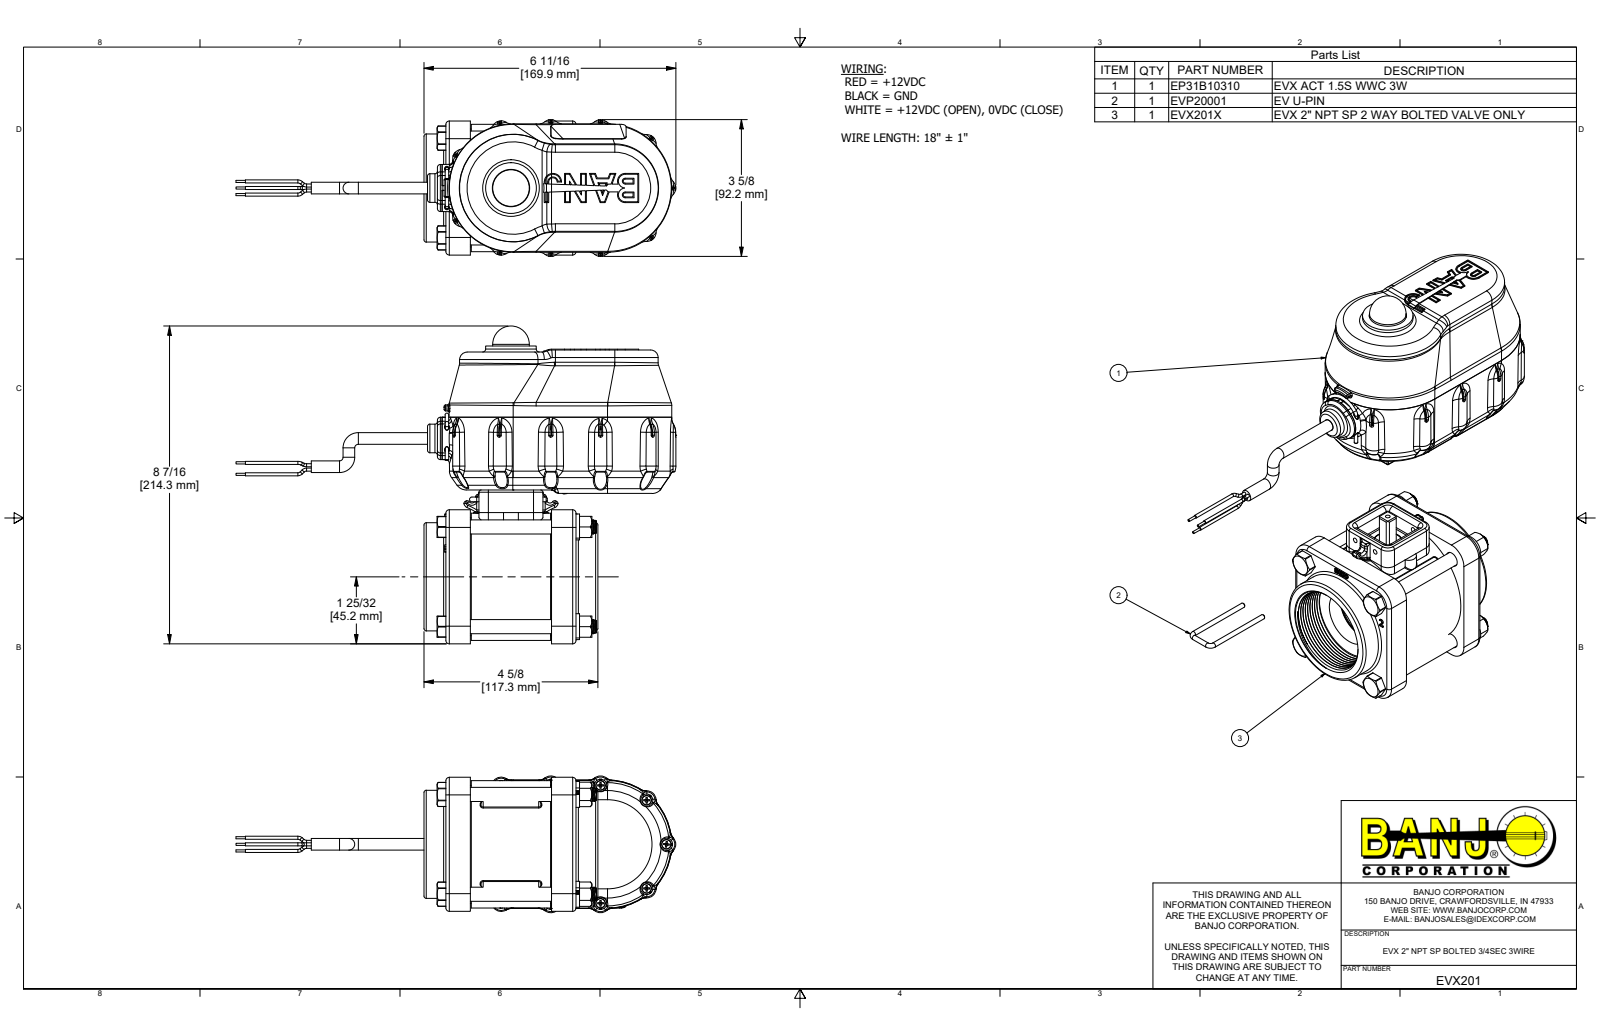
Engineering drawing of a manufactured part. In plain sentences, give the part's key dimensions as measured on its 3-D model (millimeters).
The part is named "EVX201; EVX201X; MEVX20254A; MEVX20254AX (+8 more)". Its 3-D file was written by "Autodesk Inventor 2019 (AUTOMOTIVE_DESIGN)". It is 96 solids with 11289 faces: 2906 planar, 3341 cylindrical and 5042 other. Overall it measures 296.8 by 214.3 by 92.2 millimeters. Its volume is 984 400 cubic millimeters and its surface area 425 900 square millimeters. Round holes: 11 of diameter 2.4, 11 of diameter 3.8, 7 of diameter 2, 4 of diameter 2.7, 4 of diameter 3.2, 4 of diameter 3.5, 4 of diameter 3.8, 4 of diameter 3.8, 4 of diameter 4.3, 4 of diameter 7.8, 4 of diameter 9.8, 4 of diameter 10.3. Round bosses or shafts: 60 of diameter 8.2, 17 of diameter 6.4, 15 of diameter 2, 11 of diameter 3.6, 11 of diameter 2.7, 11 of diameter 2.2, 6 of diameter 1.5, 5 of diameter 9.5. Partial cylindrical surfaces (rounded edges, fillets, slot ends): 180 of radius 0.3, 145 of radius 1, 84 of radius 0.3, 78 of radius 0.5, 53 of radius 0.1, 30 of radius 0.8, 28 of radius 1.5, 28 of radius 2. The main face-to-face distances are 2.5, 65.2, 1.5, 16.5, 71.3, 18.5, 5.4, 3.8, 48.2, 46.6. The hole center spacings are 47.5, 67.3, 68.3, 69, 42.2, 45.1, 53, 69.3.
